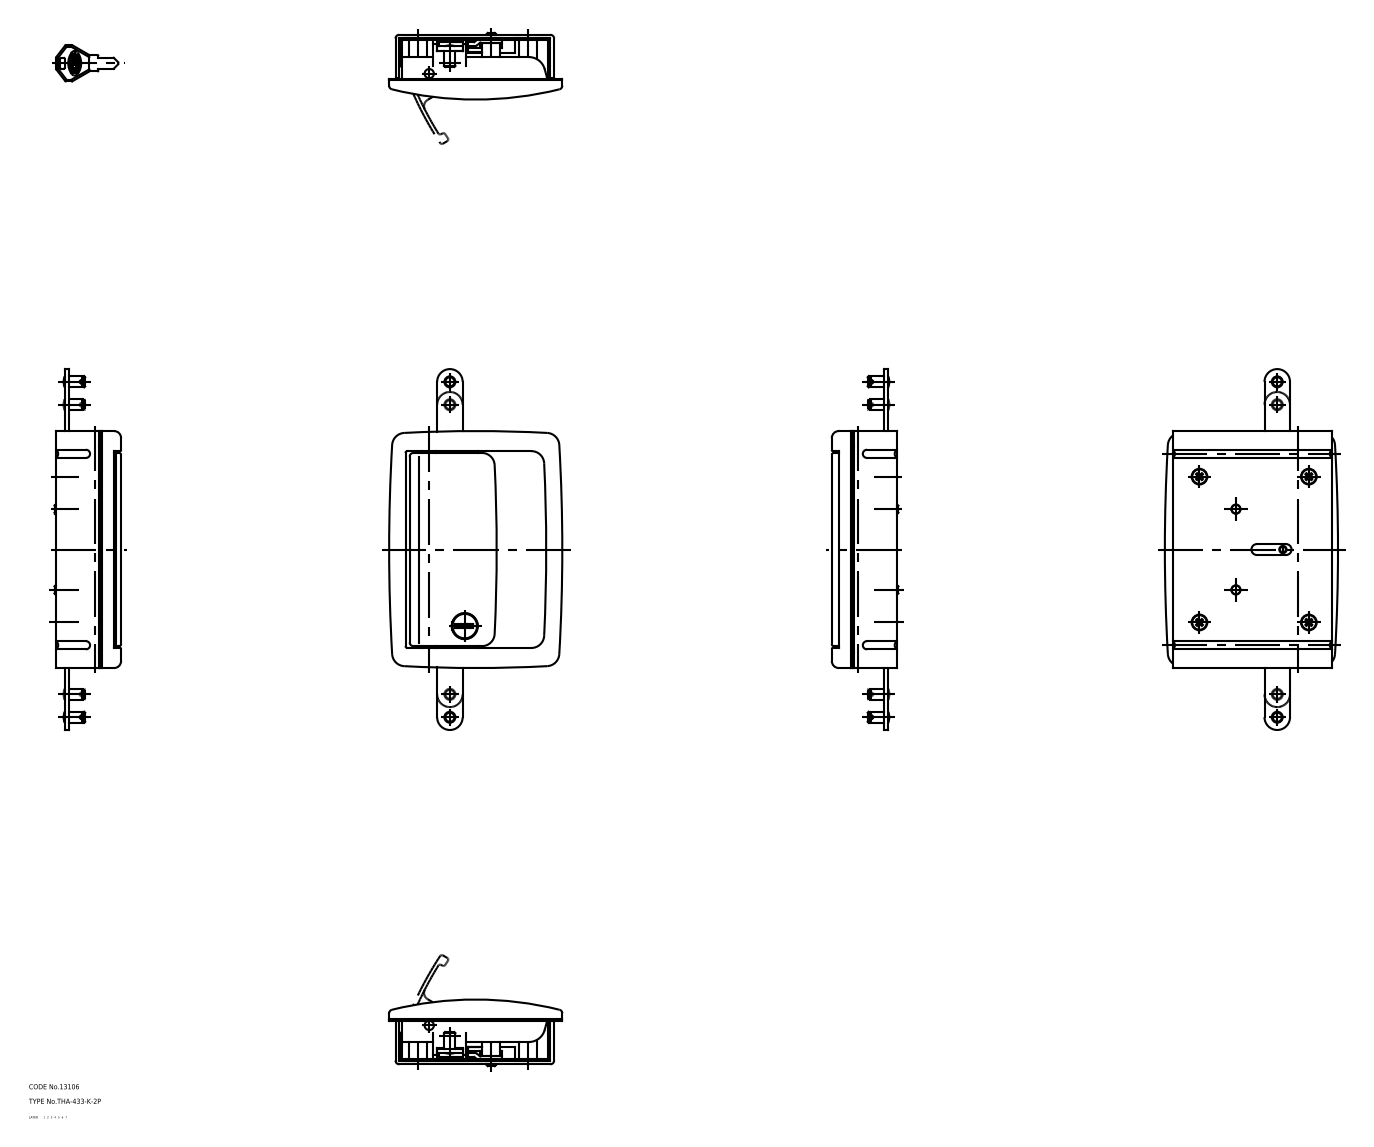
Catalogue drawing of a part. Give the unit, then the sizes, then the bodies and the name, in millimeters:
Units: millimetres
Overall size (bounding box): 198 × 102.41 × 95
Volume: 139 200 mm³ · Surface area: 115 890 mm²
Bodies: 16 solids, 651 faces (0 planar, 0 cylindrical, 651 other)
Part name (STEP PRODUCT): link_B; link_C_mr; pin_mr; pin_1_mr (+8 more)
STEP written by: CADfix (AUTOMOTIVE_DESIGN)
